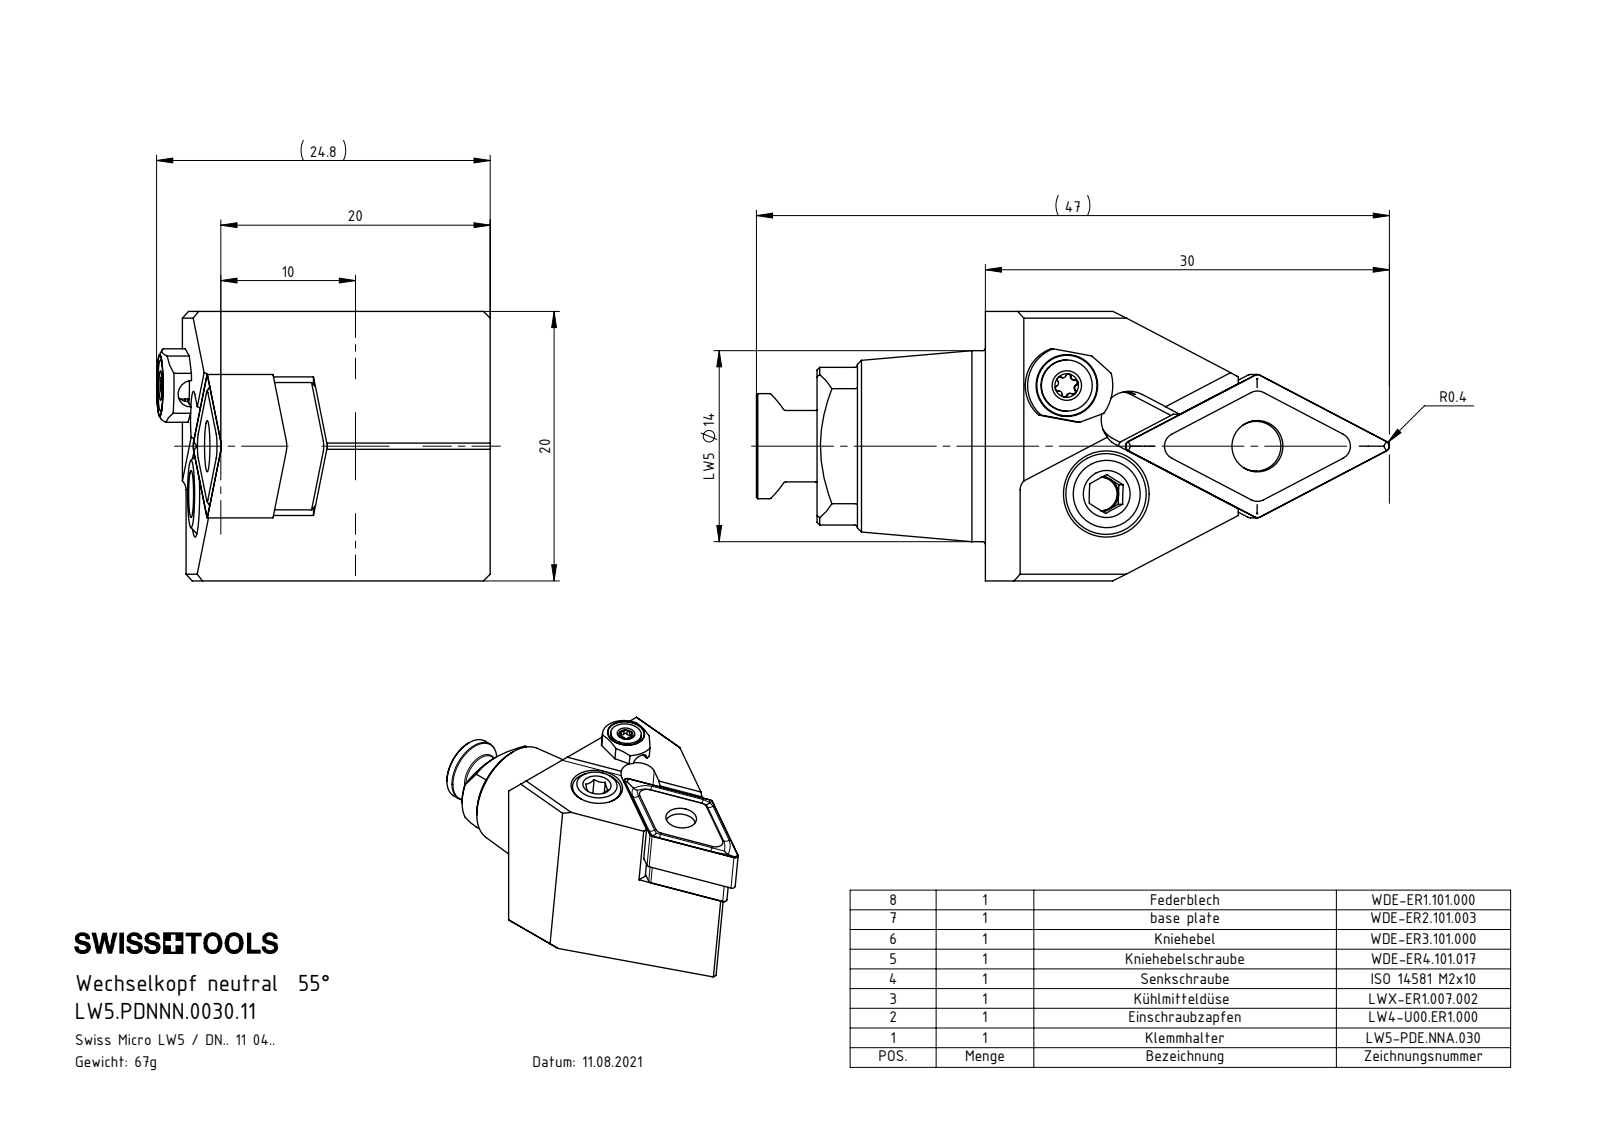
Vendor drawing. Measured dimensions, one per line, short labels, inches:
name: WDE-ER2.101.003_A; LW5.PDNNN.0030.11; ISO 14581 - M2x10; LW4-U00.ER1.000_B (+5 more)
written by: SolidWorks 2022 (CONFIG_CONTROL_DESIGN)
unit: in
bodies: 8 solids, 329 faces (120 planar, 88 cylindrical, 121 other)
size: 1.85 × 0.903 × 0.787
volume: 0.542 in³; area: 9.099 in²
holes: 2× ⌀0.098, 1× ⌀0.063, 1× ⌀0.079, 1× ⌀0.118, 1× ⌀0.15, 1× ⌀0.189, 1× ⌀0.197, 1× ⌀0.217, 1× ⌀0.252
bosses: 2× ⌀0.236, 1× ⌀0.558, 1× ⌀0.303, 1× ⌀0.232, 1× ⌀0.209, 1× ⌀0.197, 1× ⌀0.15, 1× ⌀0.113
rounds: 8× R0.008, 6× R0.009, 4× R0.016, 4× R0.031, 4× R0.083, 1× R0.02, 1× R0.059, 1× R0.072
face distances: 0.787, 0.342, 0.012, 0.021, 0.194, 0.354, 0.165, 0.182, 0.321, 0.156
hole spacings: 0.341, 0.341, 0.464, 0.465, 0.595
